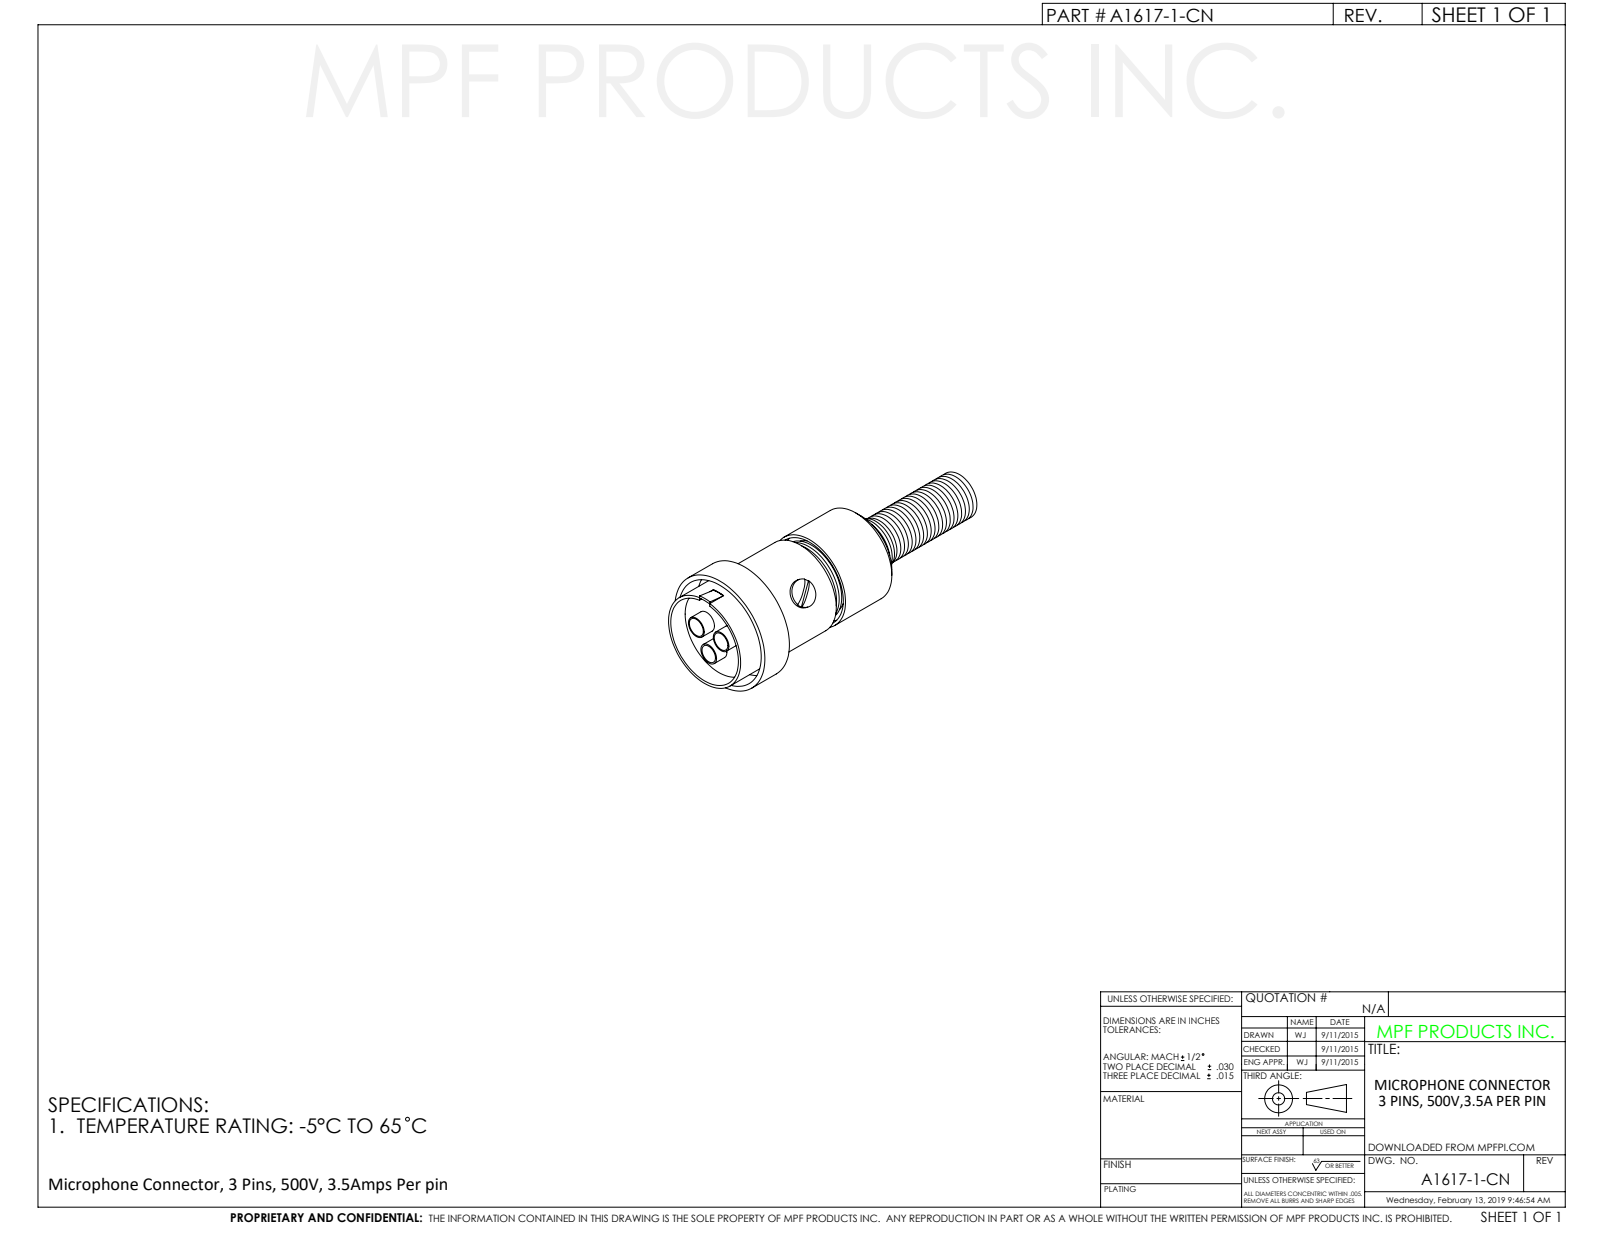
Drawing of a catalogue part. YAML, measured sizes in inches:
part_name: "A1617-1-CN"
step_written_by: "SolidWorks 2012 (CONFIG_CONTROL_DESIGN)"
units: inches
bodies: {solids: 28, faces: 207, planar: 36, cylindrical: 40, other: 131}
overall_size: [2.482, 0.875, 0.875]
volume: 0.57
surface_area: 9.956
round_holes:
  - {diameter: 0.119, count: 3}
  - {diameter: 0.087, count: 2}
  - {diameter: 0.091, count: 1}
  - {diameter: 0.131, count: 1}
  - {diameter: 0.132, count: 1}
  - {diameter: 0.136, count: 1}
  - {diameter: 0.658, count: 1}
  - {diameter: 0.803, count: 1}
round_bosses_or_shafts:
  - {diameter: 0.07, count: 2}
  - {diameter: 0.875, count: 1}
  - {diameter: 0.7, count: 1}
  - {diameter: 0.55, count: 1}
  - {diameter: 0.153, count: 1}
  - {diameter: 0.152, count: 1}
  - {diameter: 0.151, count: 1}
  - {diameter: 0.083, count: 1}
face_to_face_distances: [1.38, 1.133, 0.247, 0.59, 0.543, 0.79, 1.19, 0.6, 0.057, 0.19]
hole_center_spacings: [0.204, 0.127, 0.122, 0.128, 0.24, 0.241]
